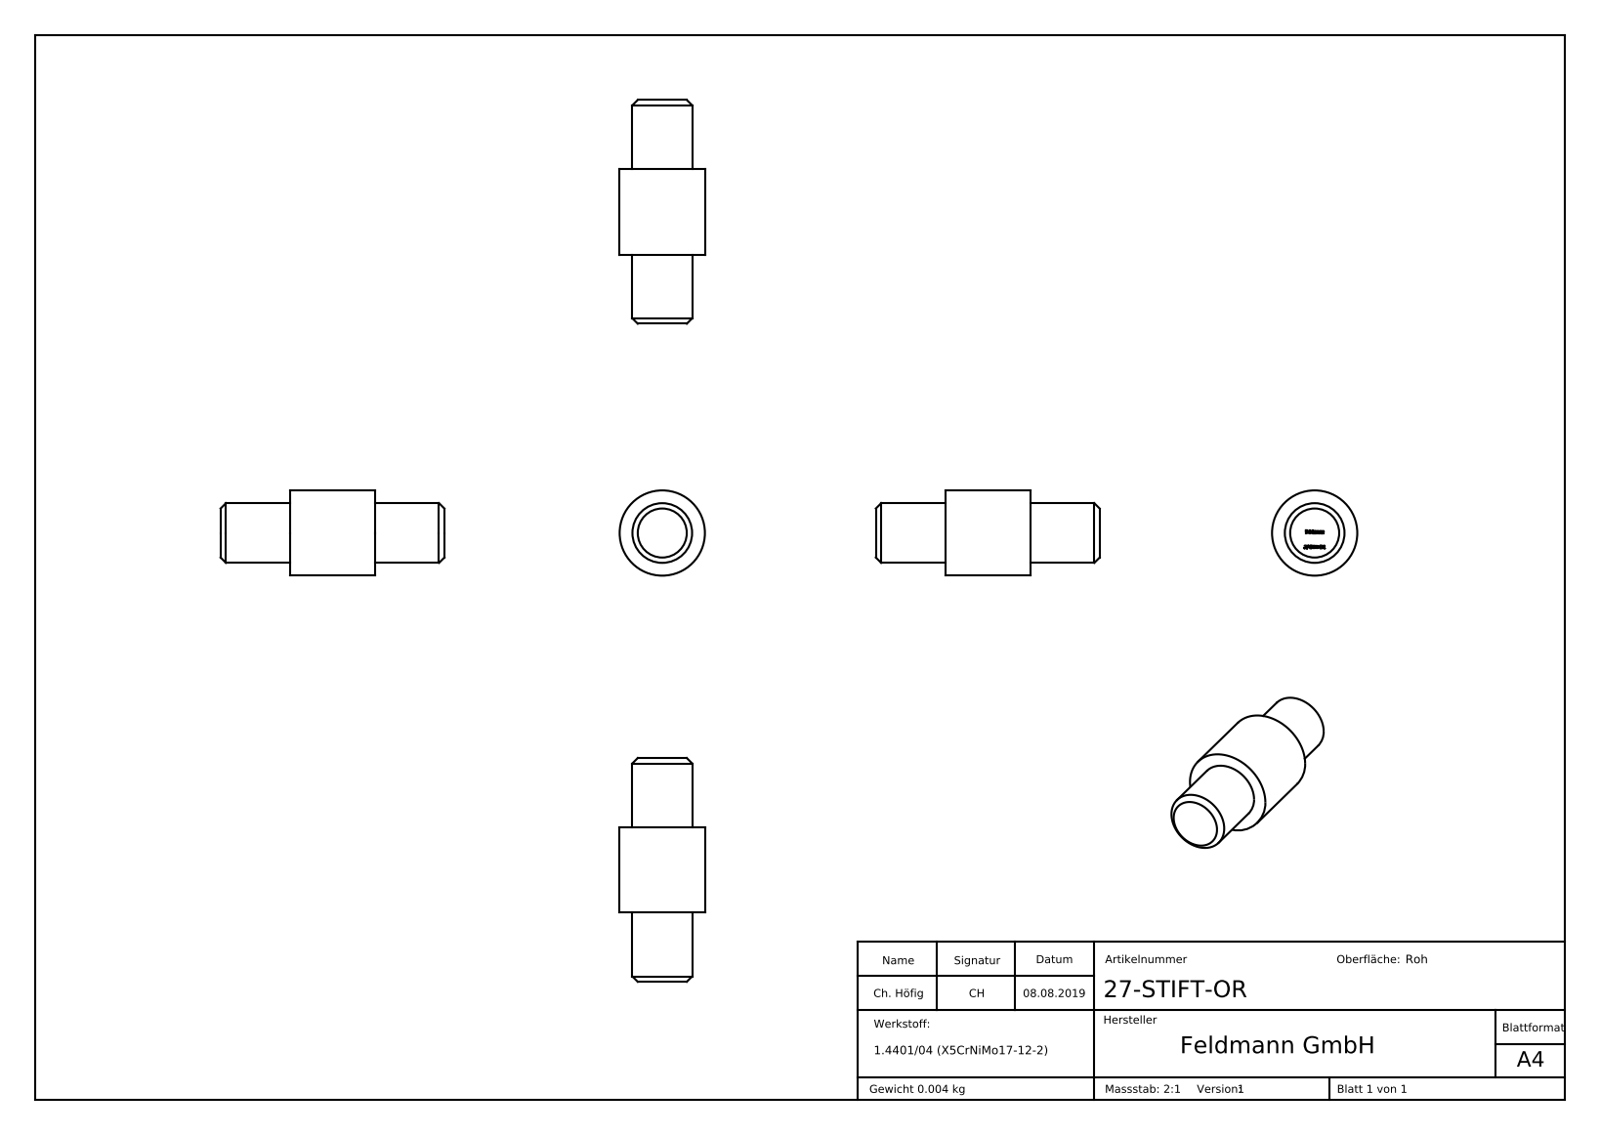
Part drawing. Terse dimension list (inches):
name: 27-Stift Teil1_27-STIFT-OR Teil1; 27-Stift Teil2_27-STIFT-OR Teil2; 27-STIFT-OR
written by: SolidWorks 2015 (CONFIG_CONTROL_DESIGN)
unit: in
bodies: 2 solids, 237 faces (145 planar, 6 cylindrical, 86 other)
size: 0.827 × 0.315 × 0.315
volume: 0.044 in³; area: 1.24 in²
holes: 1× ⌀0.22
bosses: 1× ⌀0.315
face distances: 0.256, 0.571, 0.315, 0.827, 0.252, 0.567, 0.823, 0.026, 0.016, 0.057
